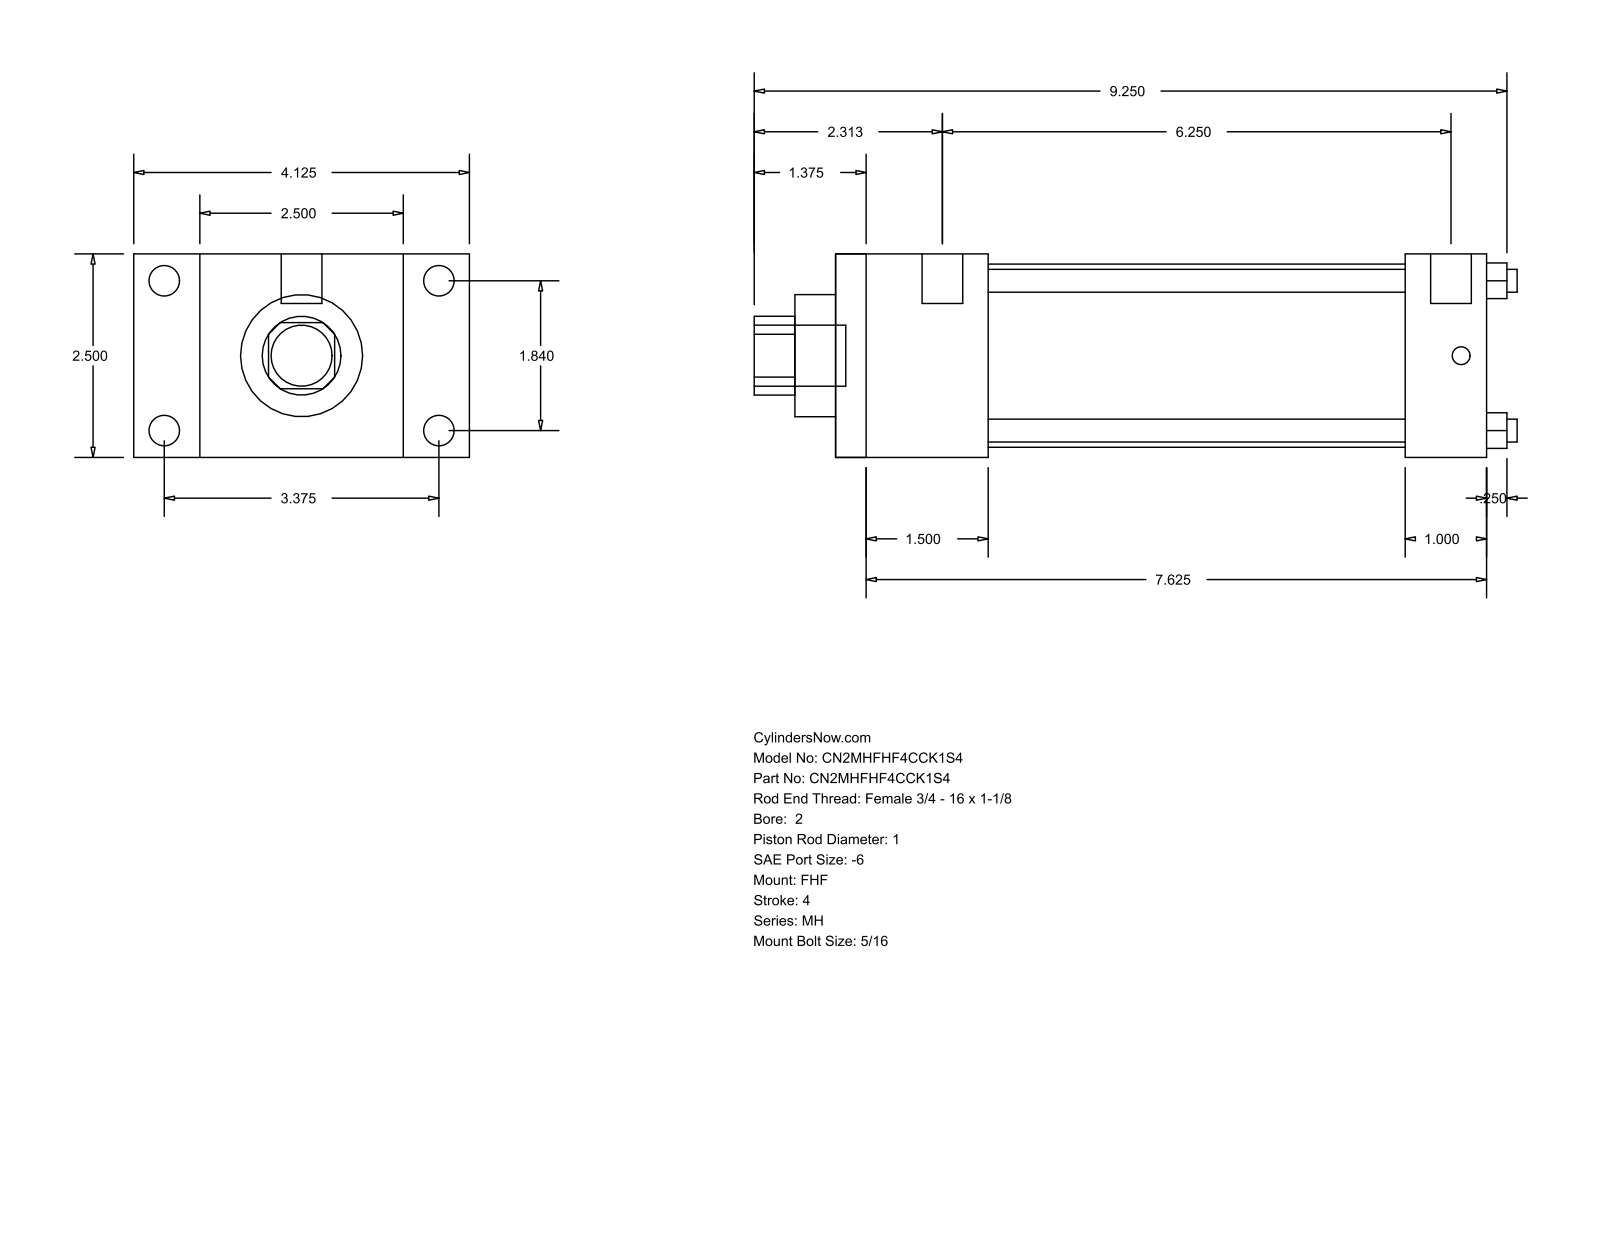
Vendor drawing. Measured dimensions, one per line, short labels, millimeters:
name: MH_FHF__0200_1
written by: GSSL Pune (CONFIG_CONTROL_DESIGN)
unit: mm
bodies: 0 solids, 88 faces (60 planar, 28 cylindrical, 0 other)
size: 238.12 × 104.78 × 63.5
holes: 4× ⌀7.14, 1× ⌀25.4, 1× ⌀38.1, 1× ⌀57.15
bosses: 4× ⌀9.53, 4× ⌀5.56, 2× ⌀12.7, 1× ⌀19.05
rounds: 1× R12.29
face distances: 63.5, 203.2, 47.63, 155.57, 20.64, 84.14, 104.78, 25.4, 177.8, 130.17
hole spacings: 33.05, 46.74, 66.1
